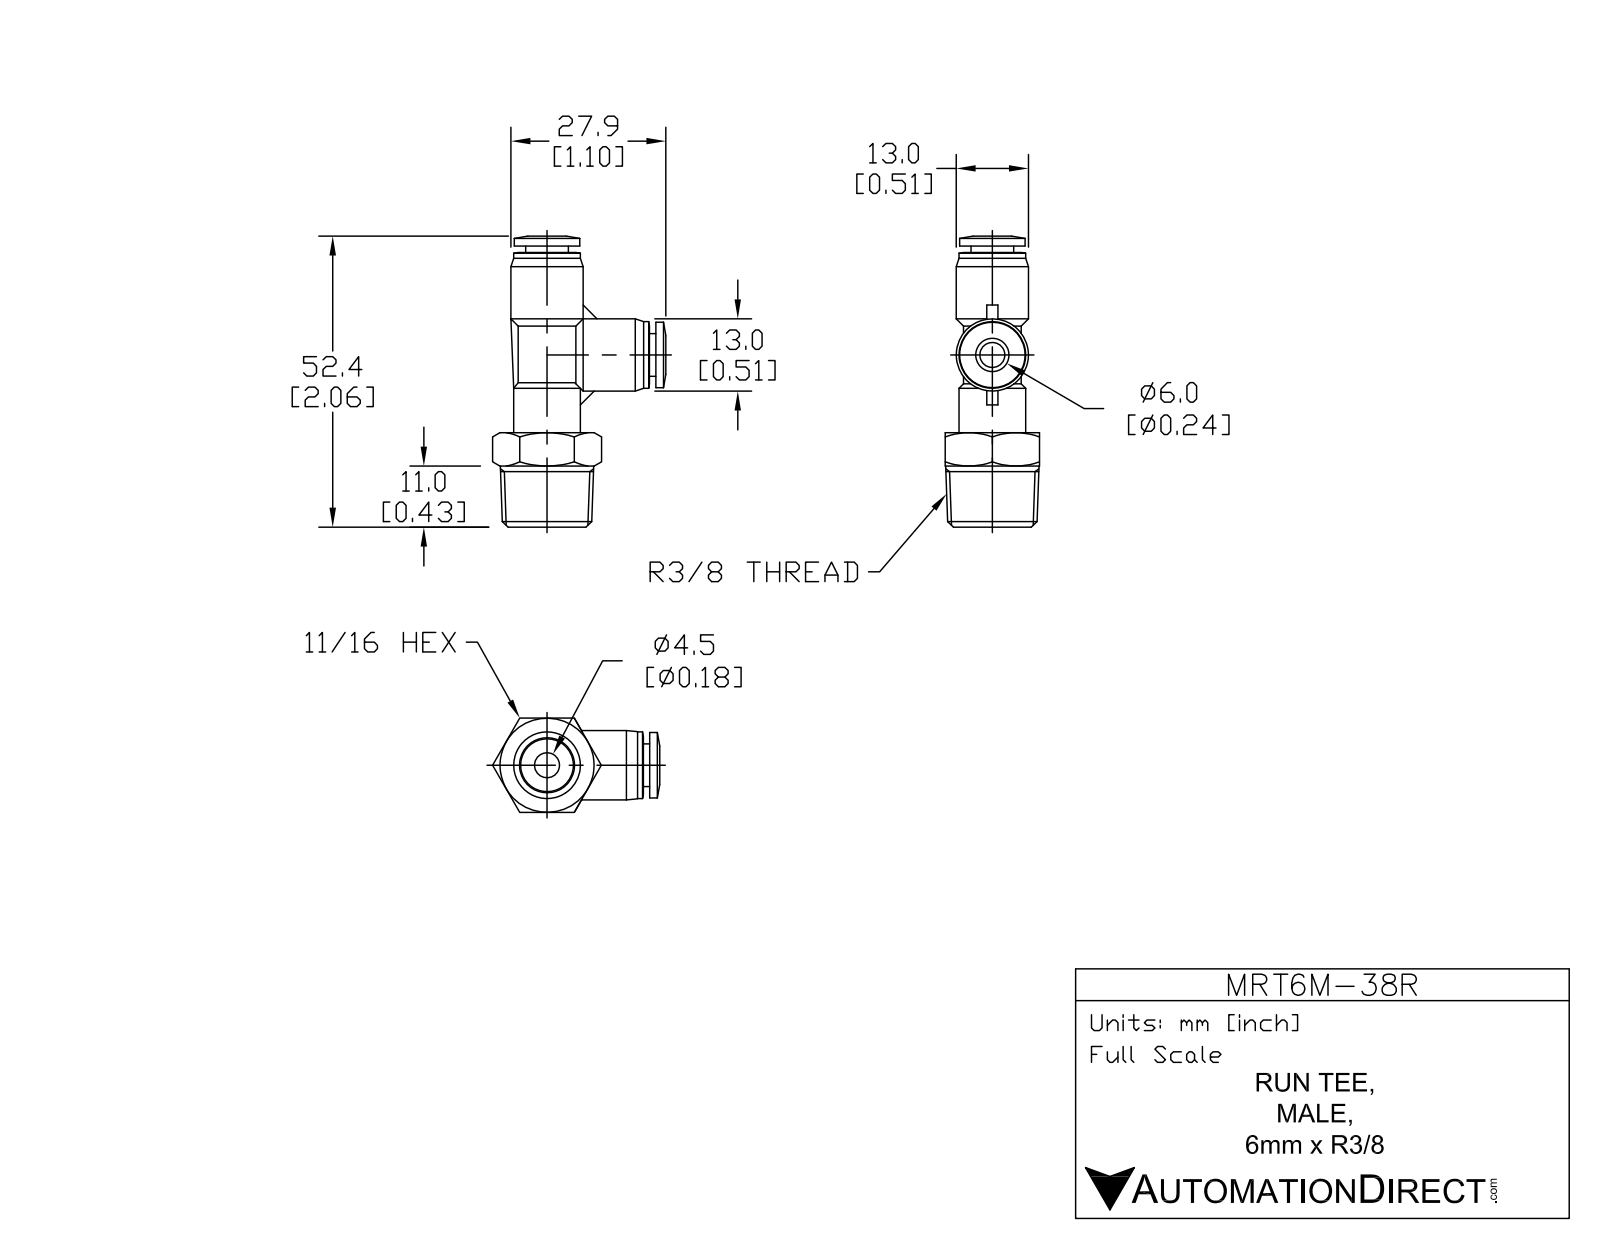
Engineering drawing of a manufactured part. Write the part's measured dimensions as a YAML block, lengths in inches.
part_name: "MRT6M-38R"
step_written_by: "SolidWorks 2015 (AUTOMOTIVE_DESIGN)"
units: inches
bodies: {solids: 1, faces: 100, planar: 25, cylindrical: 32, other: 43}
overall_size: [2.063, 1.229, 0.669]
volume: 0.495
surface_area: 7.309
round_holes:
  - {diameter: 0.157, count: 2}
  - {diameter: 0.248, count: 2}
round_bosses_or_shafts:
  - {diameter: 0.512, count: 2}
  - {diameter: 0.472, count: 2}
  - {diameter: 0.465, count: 2}
  - {diameter: 0.409, count: 2}
  - {diameter: 0.303, count: 2}
face_to_face_distances: [0.669, 0.045, 1.992, 1.323, 0.295, 0.374, 1.947, 1.278, 0.53, 0.575]
